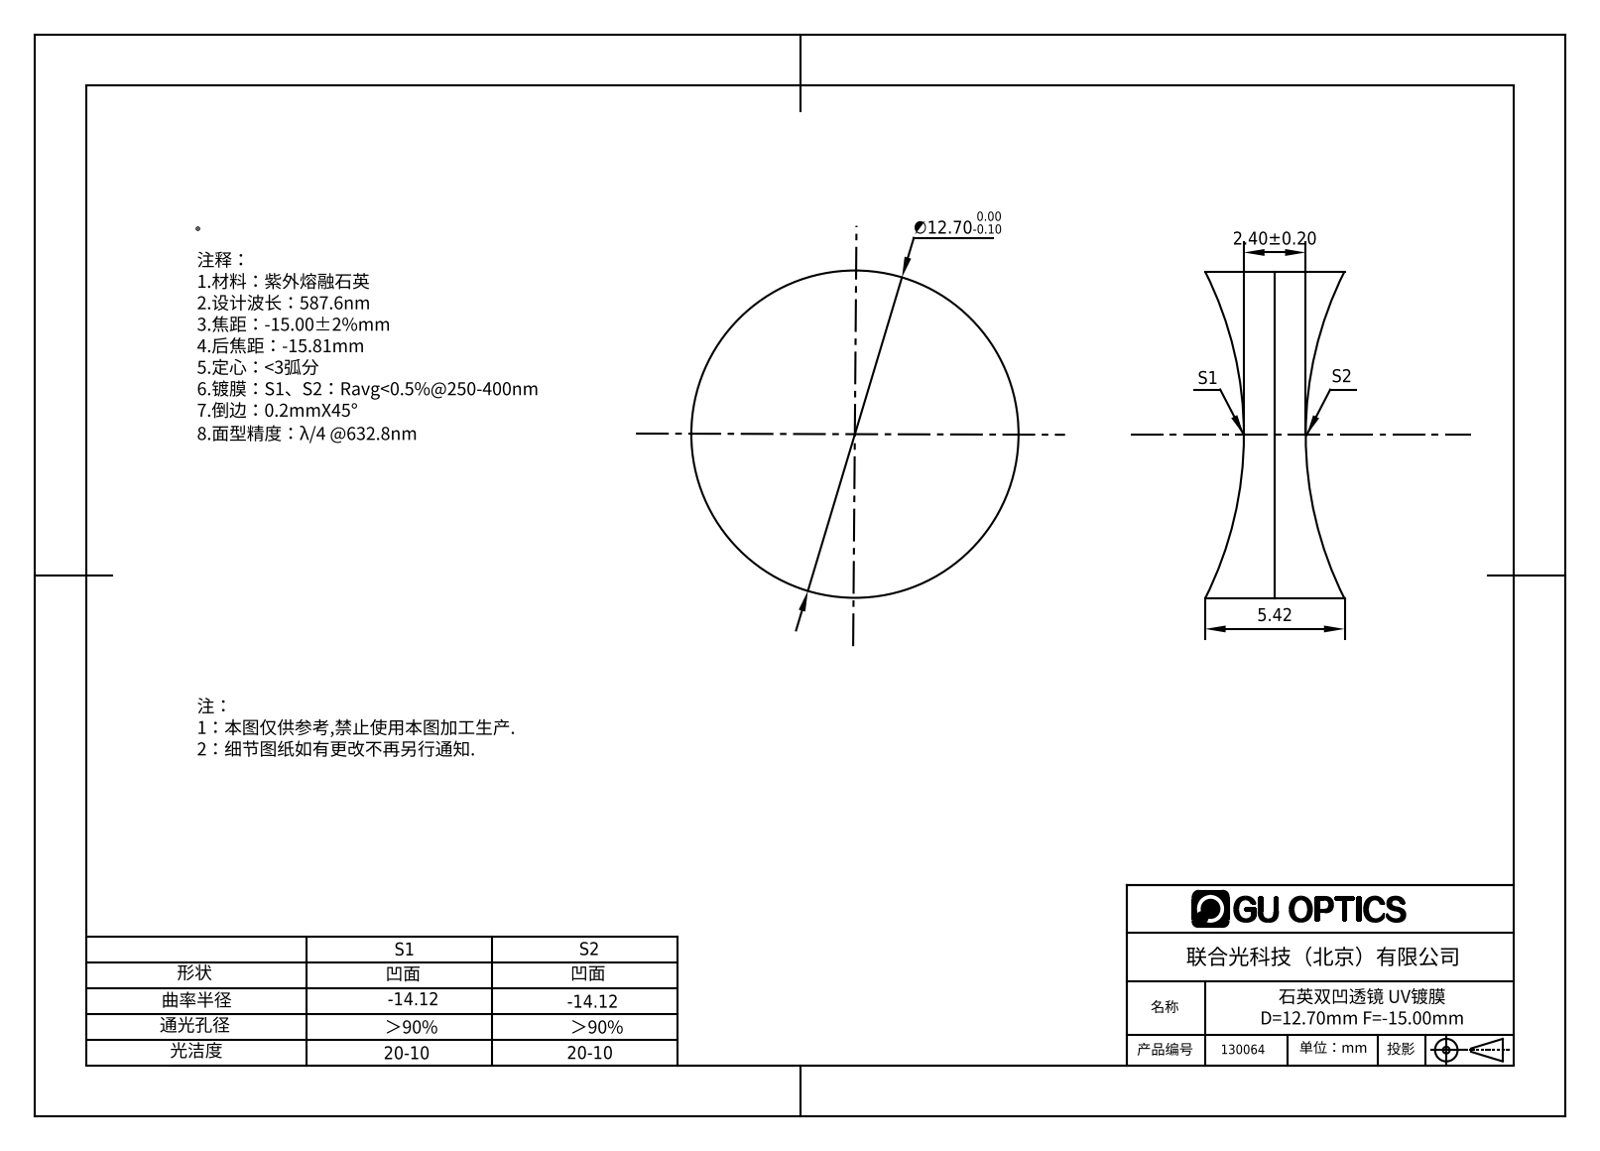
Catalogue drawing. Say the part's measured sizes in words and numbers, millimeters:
The part is named "130055". Its 3-D file was written by "SolidWorks 2016 (AUTOMOTIVE_DESIGN)". It is 1 solid with 6 faces: 0 planar, 2 cylindrical and 4 other. Overall it measures 12.7 by 12.7 by 5.42 millimeters. Its volume is 492 cubic millimeters and its surface area 484 square millimeters. Round bosses or shafts: 1 of diameter 12.7.
